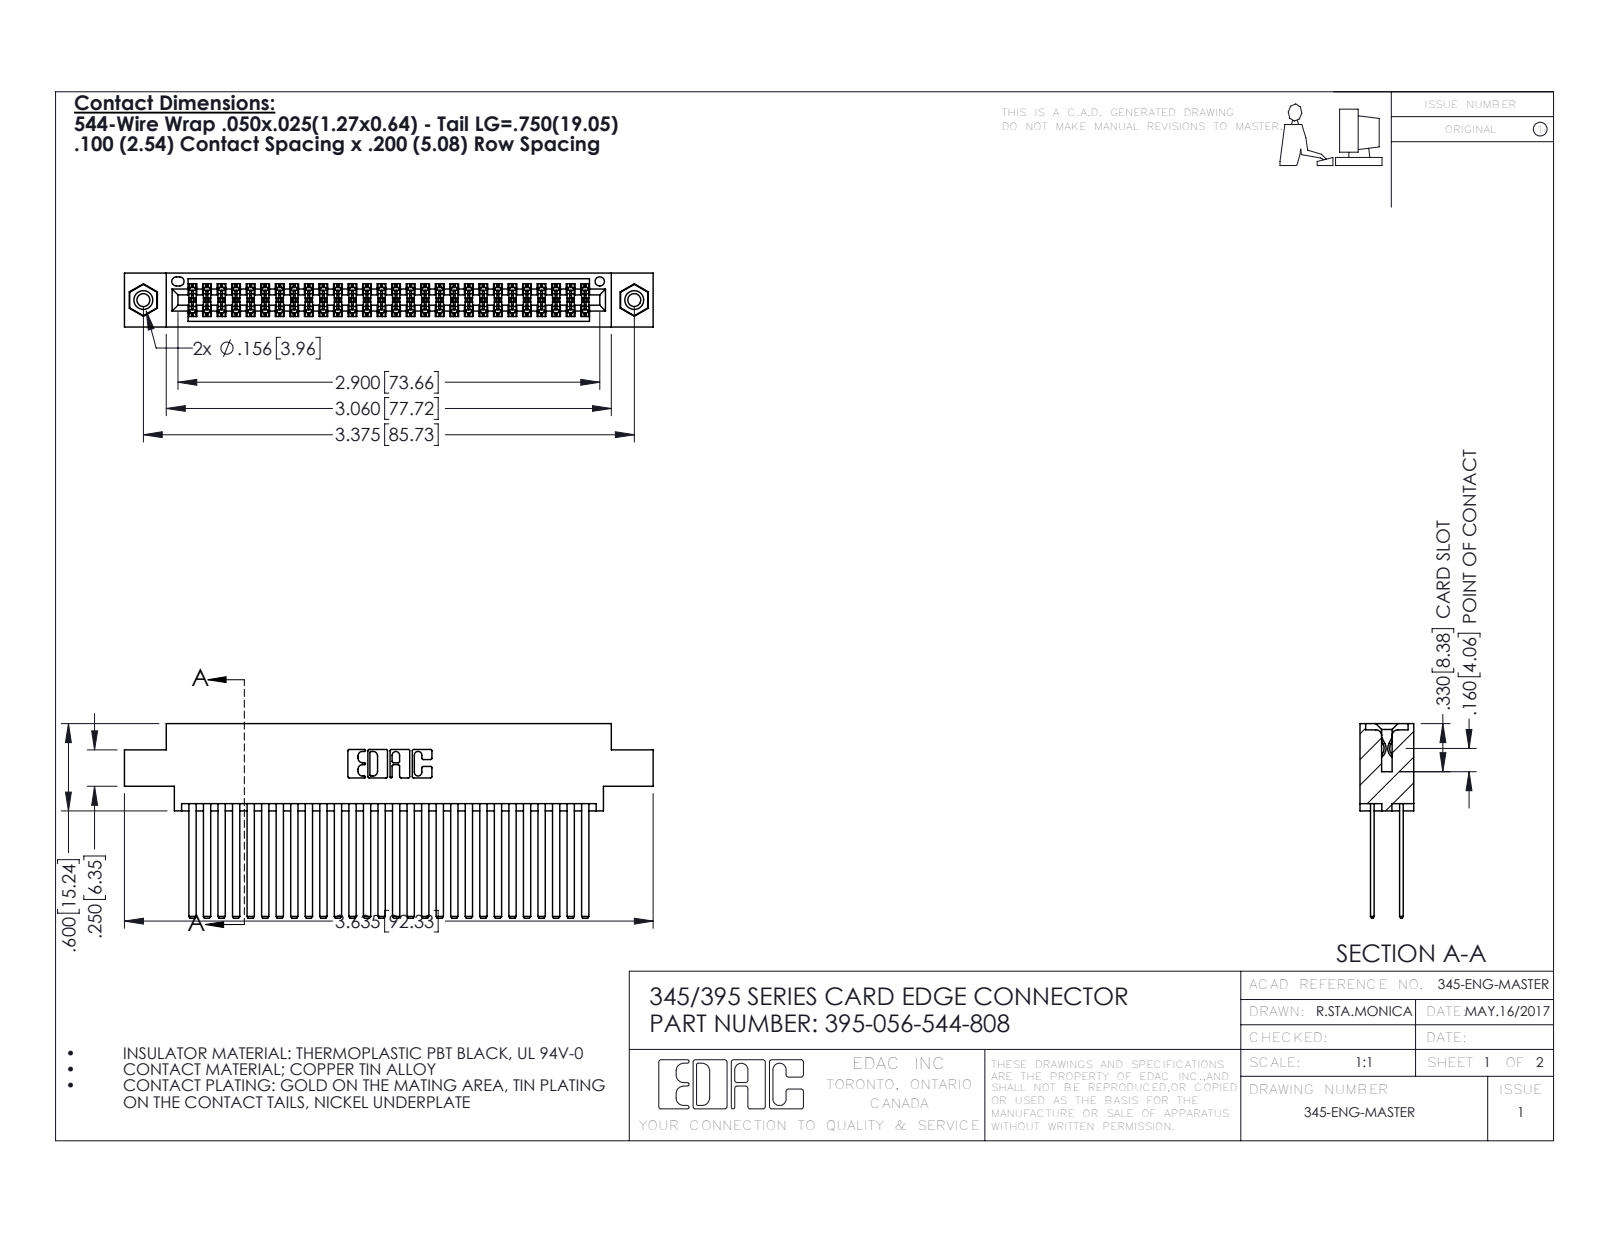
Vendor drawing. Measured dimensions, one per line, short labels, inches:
name: 345-250-001_345-250-003-102; 345 Part_0.170 Offset - 0.156 Dia-TI; 395-056-544-808; 345-292-001_345-293-144
written by: SolidWorks 2016 (CONFIG_CONTROL_DESIGN)
unit: in
bodies: 59 solids, 2654 faces (1740 planar, 898 cylindrical, 16 other)
size: 3.635 × 1.337 × 0.37
volume: 0.58 in³; area: 25.16 in²
holes: 2× ⌀0.089, 2× ⌀0.125, 2× ⌀0.156, 1× ⌀0.064
bosses: 2× ⌀0.155
rounds: 84× R0.006, 22× R0.01, 6× R0.007, 6× R0.031, 3× R0.026, 2× R0.014, 2× R0.019, 2× R0.022
face distances: 0.2, 0.025, 0.072, 0.298, 0.098, 0.272, 0.225, 0.175, 0.37, 0.15
hole spacings: 0.27, 3.14, 3.375
